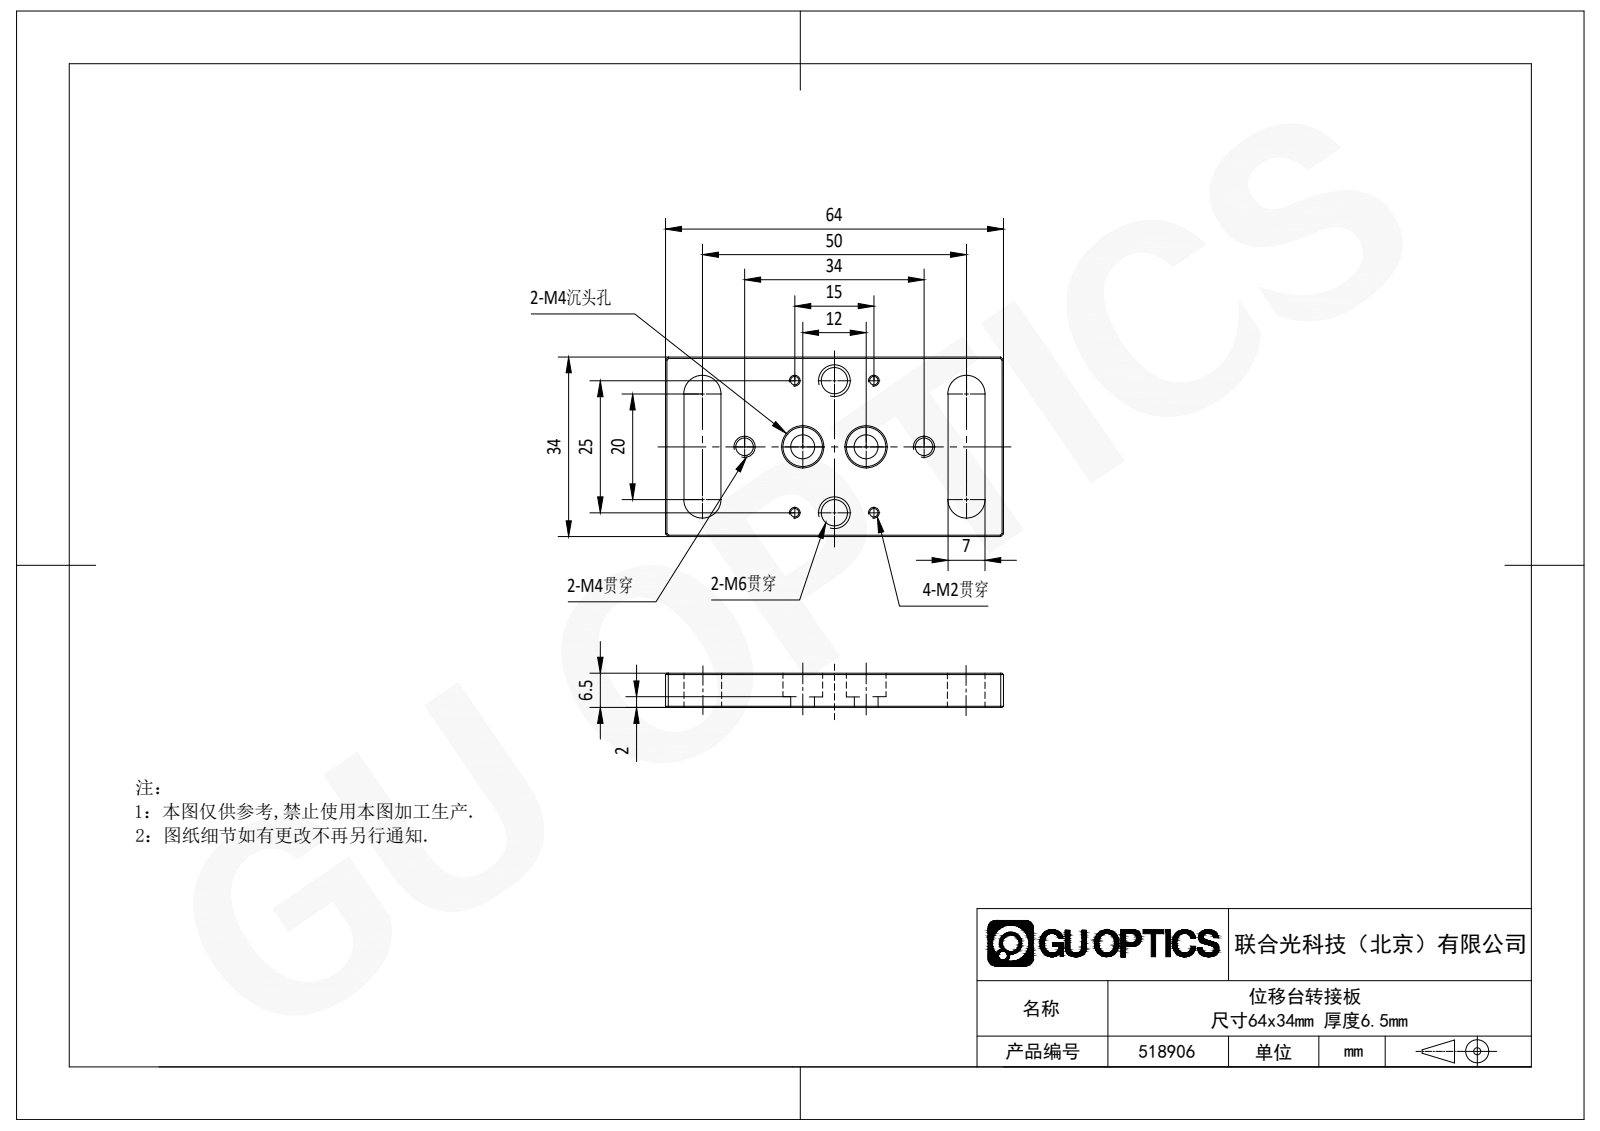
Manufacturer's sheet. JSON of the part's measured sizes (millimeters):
{"step_written_by": "SolidWorks 2020 (CONFIG_CONTROL_DESIGN)", "units": "millimeters", "bodies": {"solids": 1, "faces": 58, "planar": 32, "cylindrical": 16, "other": 10}, "overall_size": [64, 34, 6.5], "volume_mm3": 10920, "surface_area_mm2": 6176, "round_holes": [[1.6, 4], [3.3, 2], [4.5, 2], [5, 2], [7.5, 2]], "partial_cylinders_radius": [[3.5, 4]], "face_to_face_distances": [6.5, 34, 3.5, 10.5, 53.5, 60.5, 7, 50, 64, 57], "hole_center_spacings": [7.5, 12.59, 13.87, 15.7, 18.4, 21.1, 26.1, 27.5]}
